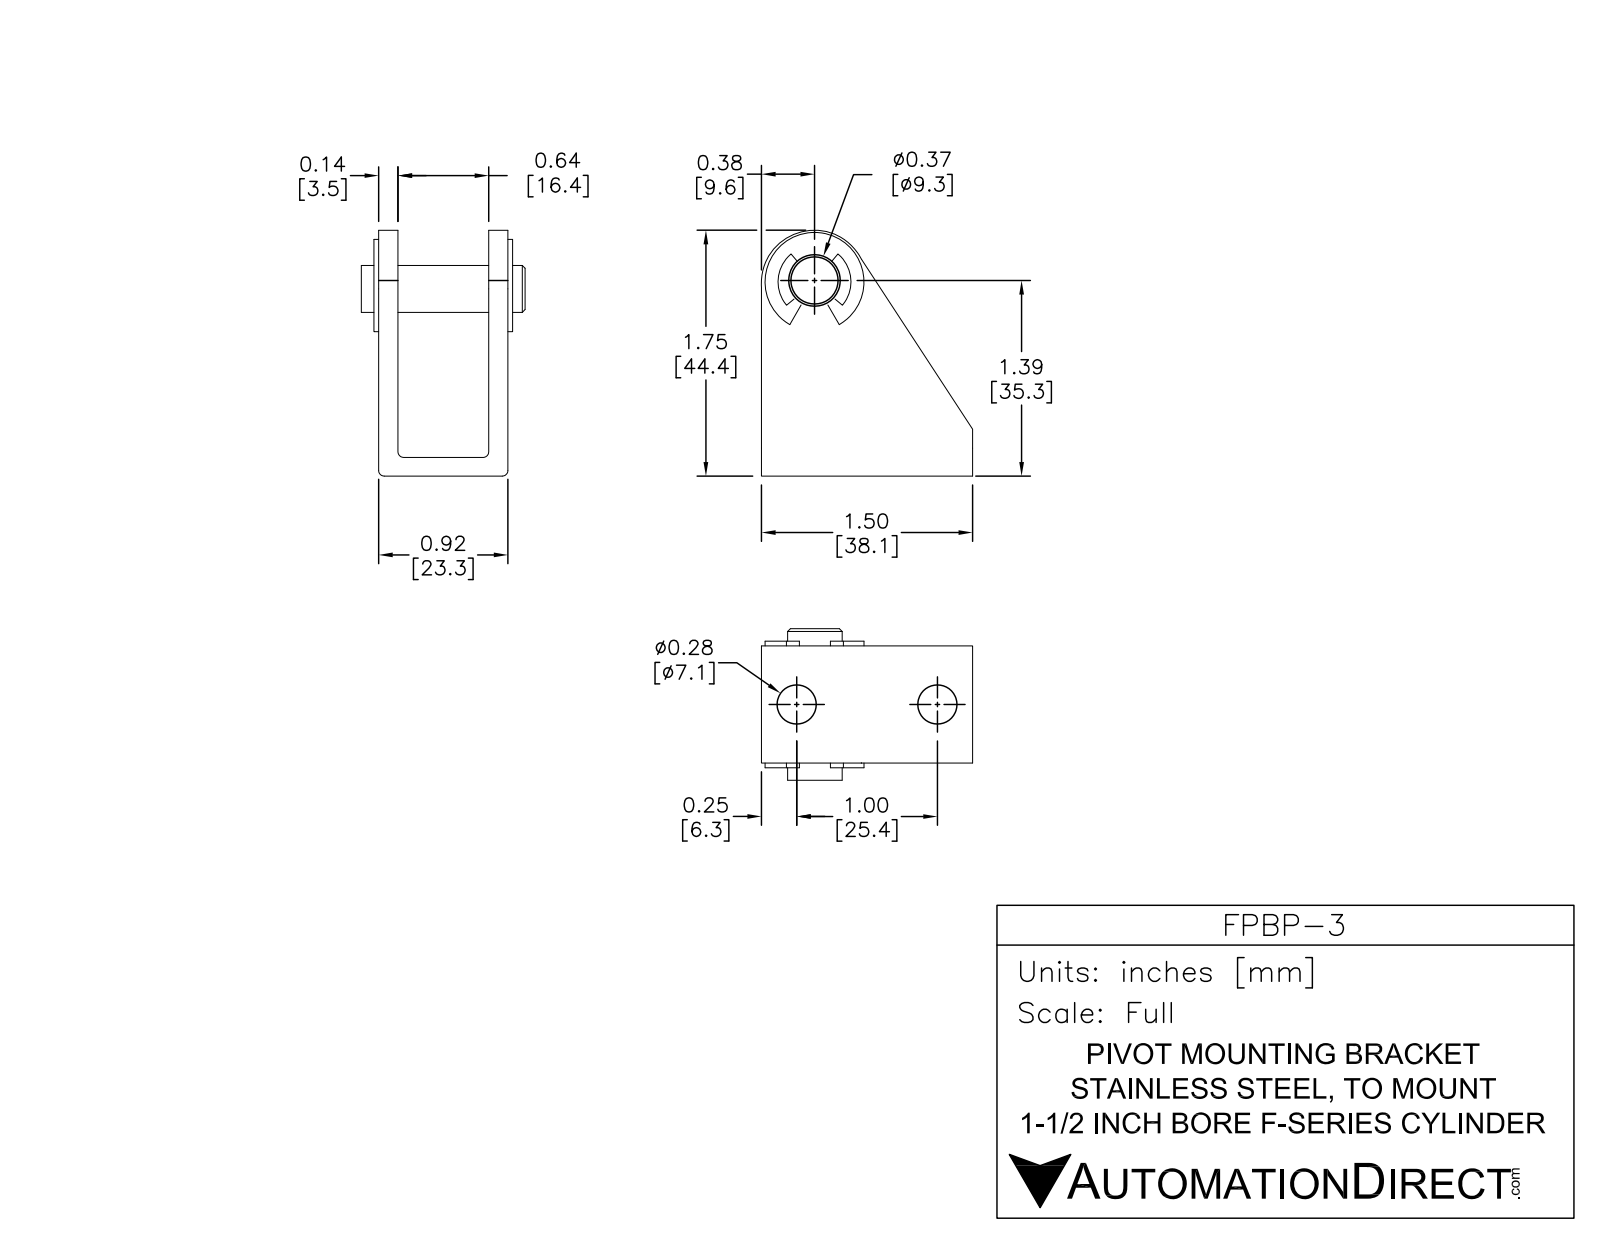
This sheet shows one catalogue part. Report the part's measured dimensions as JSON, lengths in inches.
{"part_name": "FPBP-3", "step_written_by": "SolidWorks 2017 (AUTOMOTIVE_DESIGN)", "units": "inches", "bodies": {"solids": 2, "faces": 36, "planar": 20, "cylindrical": 16, "other": 0}, "overall_size": [1.75, 1.5, 1.165], "volume_in3": 0.728, "surface_area_in2": 12.18, "round_holes": [[0.28, 2], [0.366, 1]], "round_bosses_or_shafts": [[0.37, 1]], "partial_cylinders_radius": [[0.03, 2], [0.168, 2], [0.375, 1]], "face_to_face_distances": [0.138, 0.78, 0.642, 0.917, 0.124, 0.262, 0.904, 1.041, 1.5, 1.165], "hole_center_spacings": [1]}
